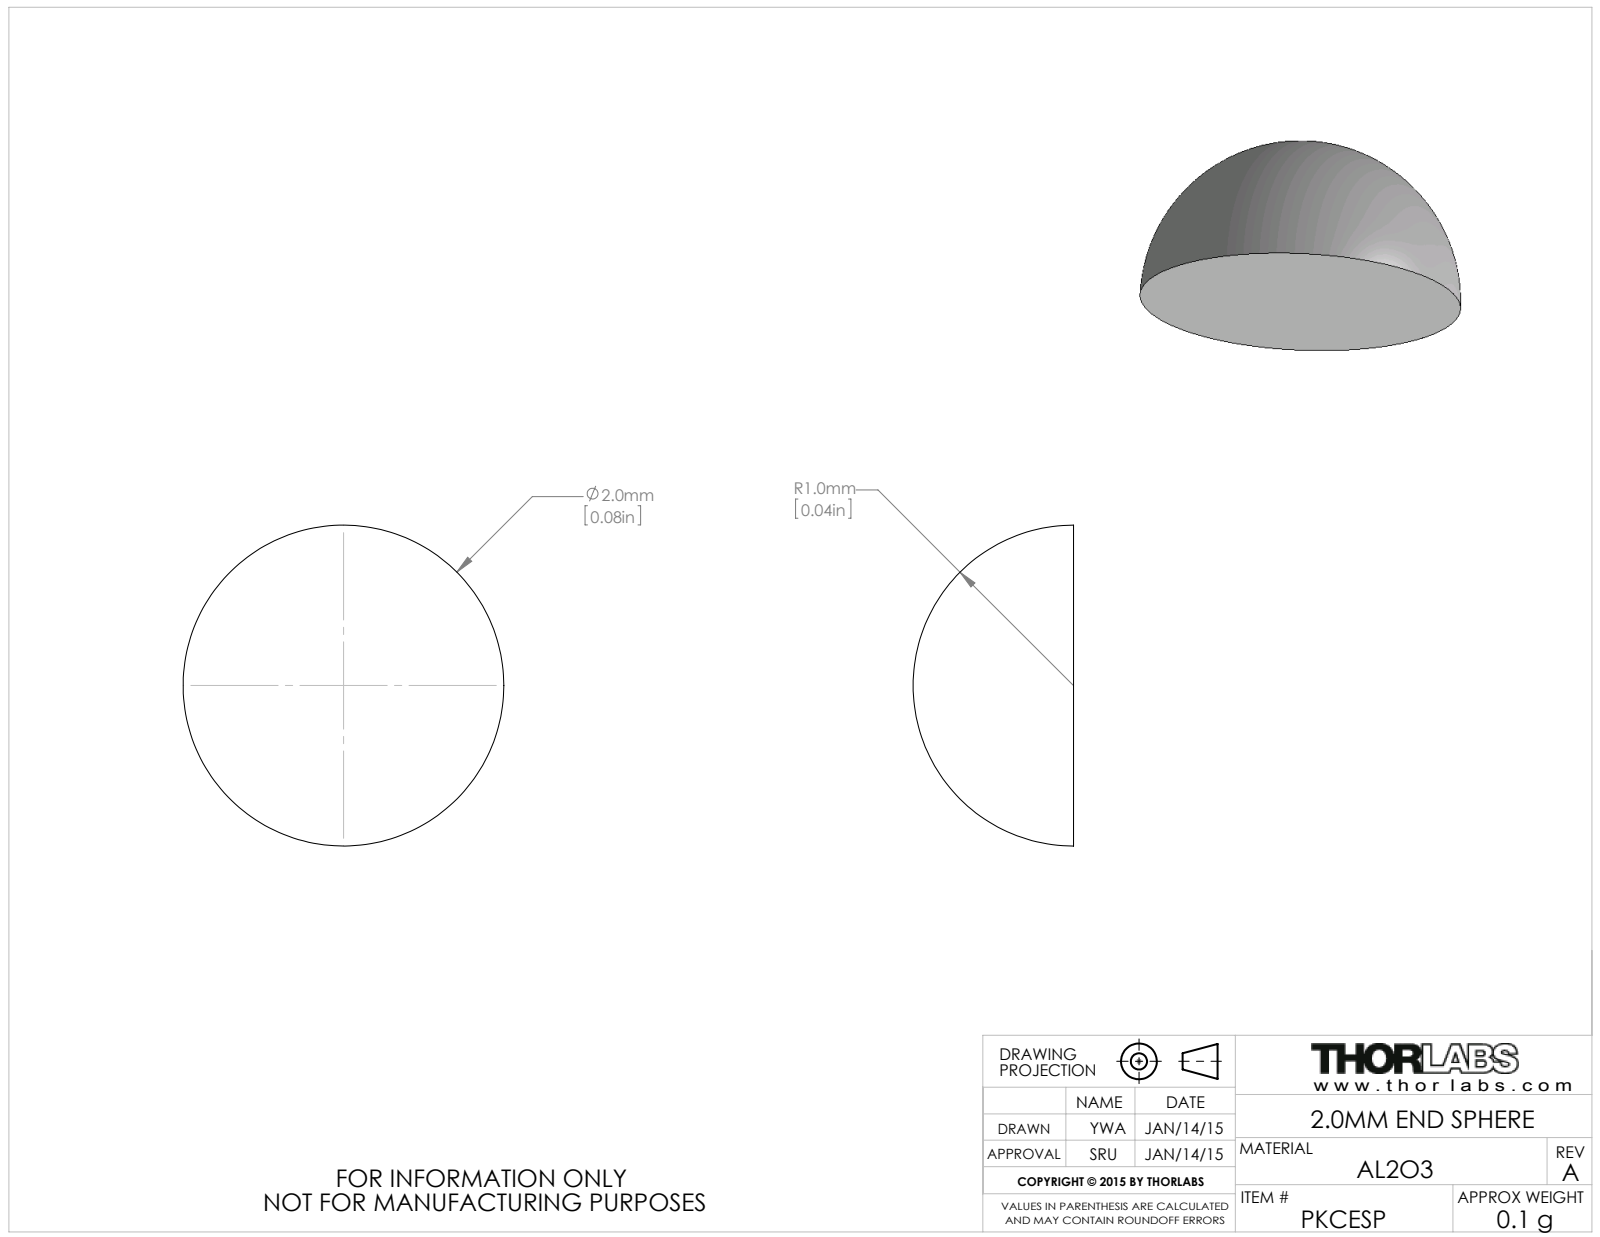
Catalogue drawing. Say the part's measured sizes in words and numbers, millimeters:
The part is named "PKCESP". Its 3-D file was written by "SolidWorks 2012 (AUTOMOTIVE_DESIGN)". It is 1 solid with 3 faces: 1 planar, 0 cylindrical and 2 other. Overall it measures 2 by 2 by 1 millimeters. Its volume is 2 cubic millimeters and its surface area 9 square millimeters.
